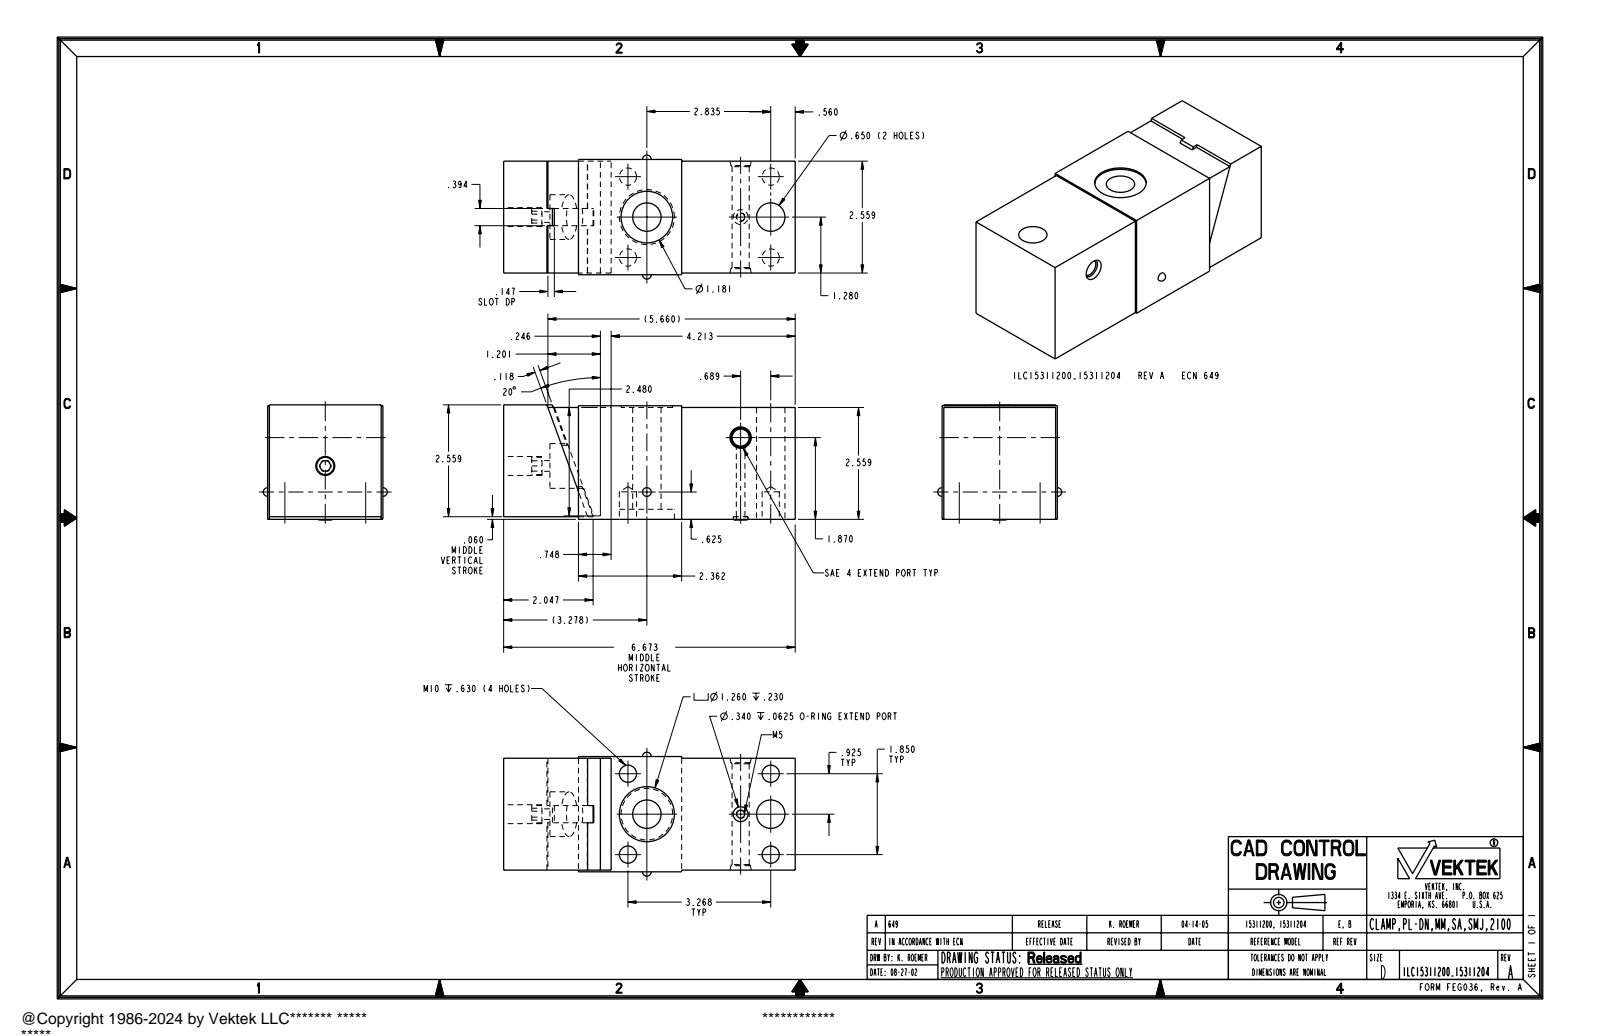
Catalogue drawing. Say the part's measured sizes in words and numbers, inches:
The part is named "ILC15311200_15311204". Its 3-D file was written by "PRO/ENGINEER BY PARAMETRIC TECHNOLOGY CORPORATION, 2004290 (AUTOMOTIVE_DESIGN_CC2)". It is 2 solids with 115 faces: 61 planar, 30 cylindrical and 24 other. Overall it measures 6.673 by 2.837 by 2.636 inches. Its volume is 39.4 cubic inches and its surface area 131 square inches. Round holes: 4 of diameter 0.394, 2 of diameter 0.65, 1 of diameter 0.197, 1 of diameter 0.244, 1 of diameter 0.34, 1 of diameter 0.392, 1 of diameter 0.433, 1 of diameter 1.024, 1 of diameter 1.181, 1 of diameter 1.26. Round bosses or shafts: 1 of diameter 0.394. The main face-to-face distances are 2.559, 2.598, 0.039, 0.06, 4.213, 2.46, 6.673, 2.214, 0.246, 4.459. The hole center spacings are 0.925, 1.022, 1.154, 1.85, 2.74, 2.982, 3.268, 3.396.
